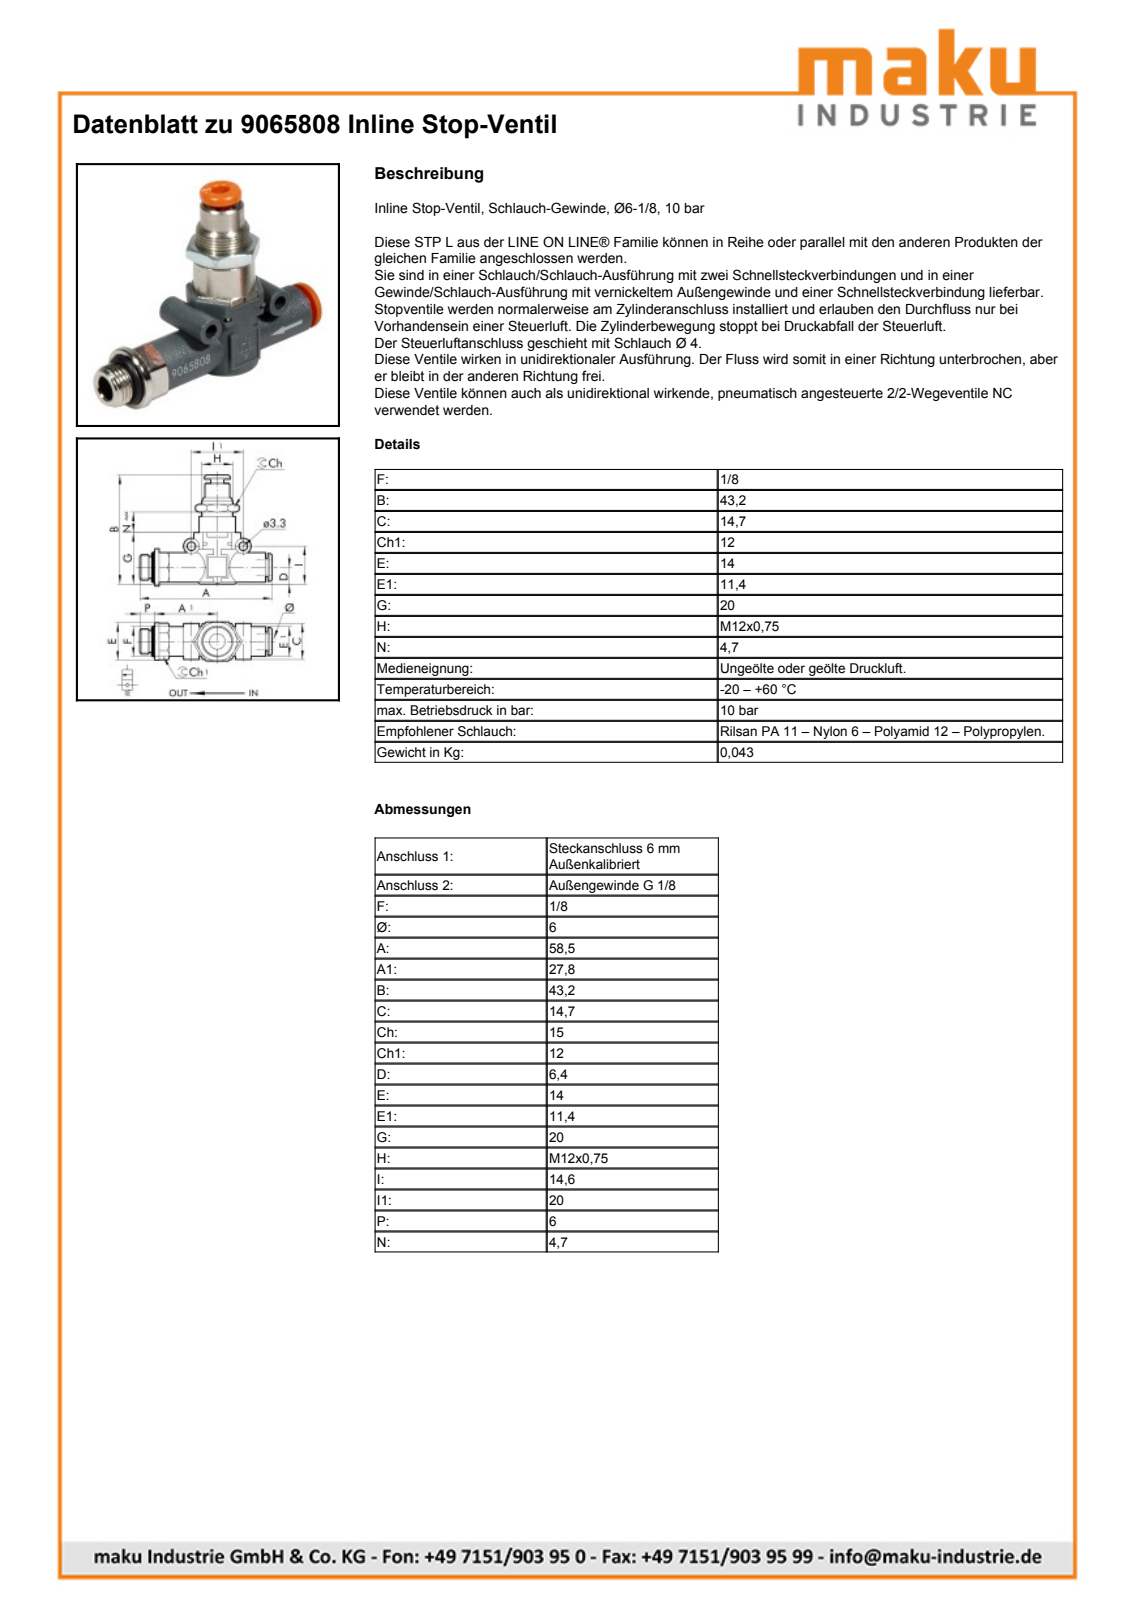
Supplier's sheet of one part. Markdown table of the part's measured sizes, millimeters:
| quantity | value |
| --- | --- |
| part name | 9065808; LINE-ON-LINE D6 PNV_L-body; LINE-ON-LINE D6 VNR-L bushing; LINE-ON-LINE D6-1/8 RML-thread port (+2 more) |
| STEP written by | PARTsolutions (AUTOMOTIVE_DESIGN) |
| units | millimeters |
| bodies | 5 solids, 186 faces (113 planar, 57 cylindrical, 16 other) |
| overall size | 58.5 × 43.8 × 14.7 |
| volume | 7 410 mm³ |
| surface area | 7 845 mm² |
| round holes (diameter × count) | 3.3 × 2, 3.5 × 1, 4 × 1, 5 × 1, 5.53 × 1, 6 × 1, 6.2 × 1, 9 × 1, 9.6 × 1, 10.3 × 1, 11.6 × 1 |
| round bosses / shafts (diameter × count) | 6 × 2, 14.8 × 1, 14 × 1, 13.8 × 1, 12 × 1, 11.4 × 1, 11 × 1, 9.73 × 1 |
| partial cylindrical surfaces (radius × count) | 3.75 × 1, 6.85 × 1, 7.9 × 1, 7.95 × 1, 9.15 × 1 |
| main face-to-face distances | 1.4, 18.4, 0.4, 17, 6.8, 14.2, 14.5, 12, 14.3, 14.6 |
| hole center spacings | 12.74, 20 |
